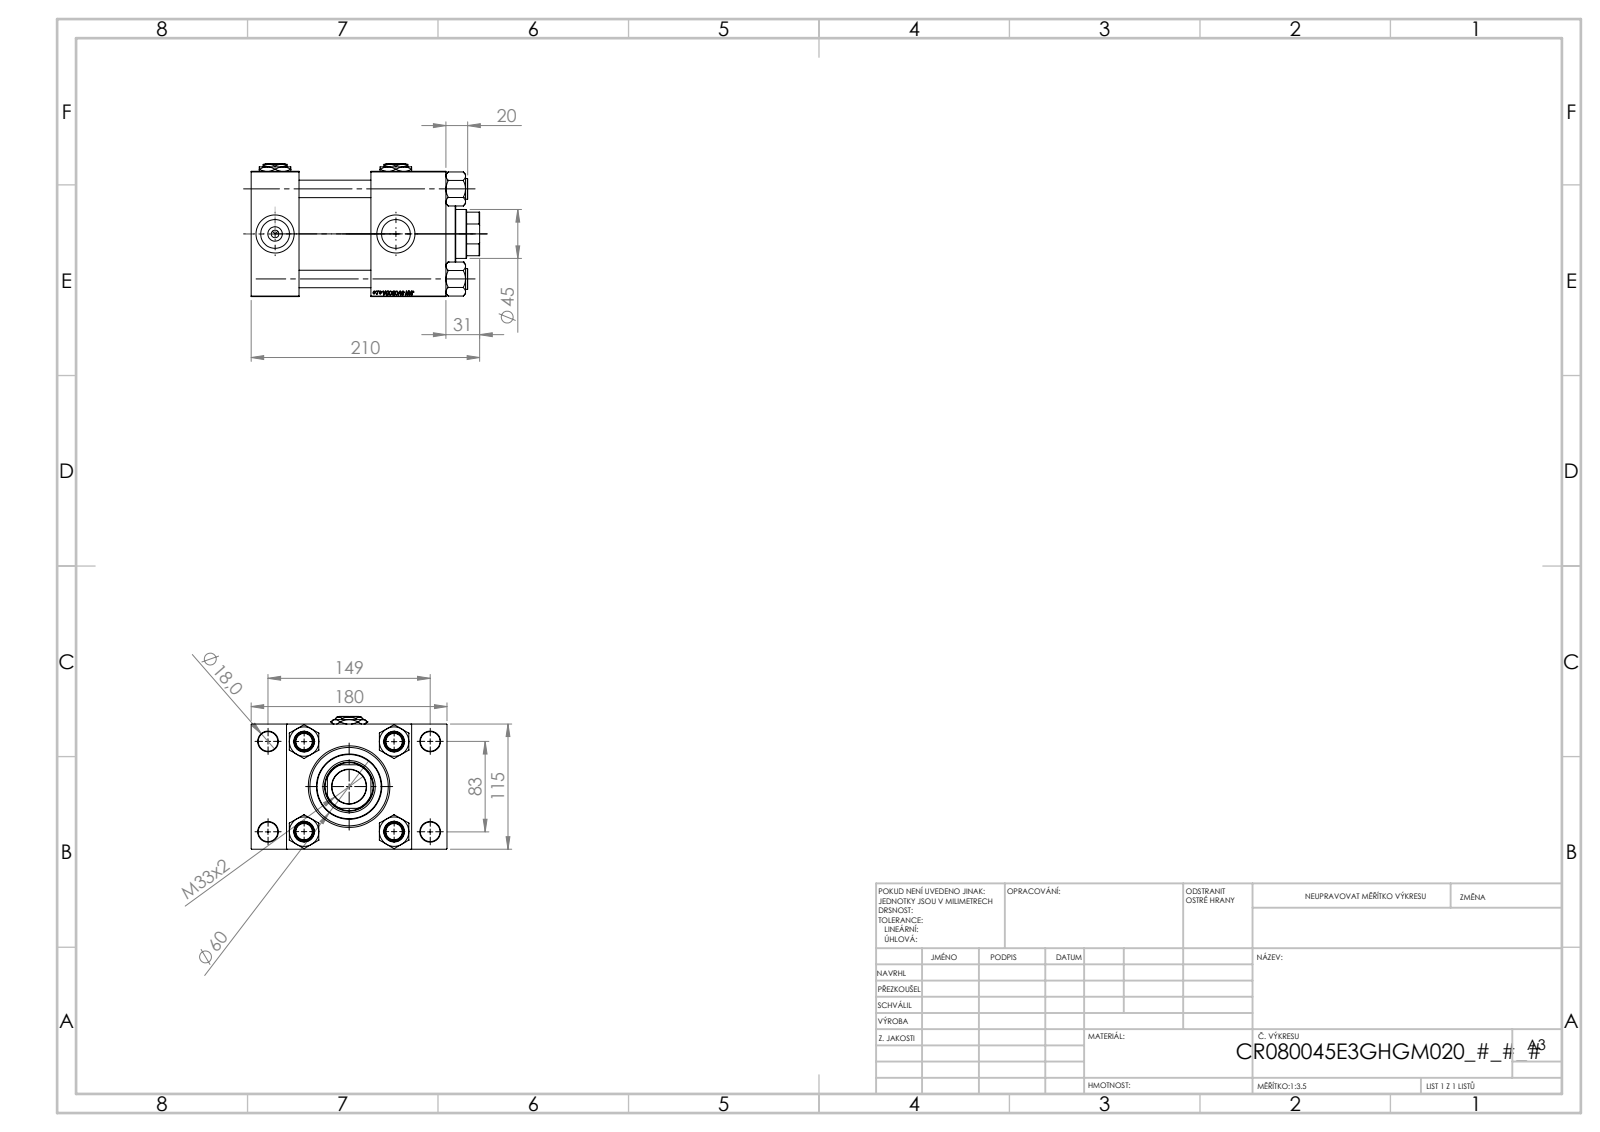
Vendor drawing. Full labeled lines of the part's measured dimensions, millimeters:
Part name (STEP PRODUCT): V215CR_VCP_E; V215CR_TYCINKA_E; Zatka_pro_OIL_PORT; NUT_M5_E (+2 more)
STEP written by: SolidWorks 2019 (CONFIG_CONTROL_DESIGN)
Units: millimetres
Bodies: 13 solids, 1290 faces (595 planar, 101 cylindrical, 594 other)
Overall size (bounding box): 210 × 180 × 122
Volume: 2 103 000 mm³ · Surface area: 322 824 mm²
Round holes (diameter × count): ⌀16 ×4, ⌀18 ×4, ⌀26.44 ×4, ⌀35 ×4, ⌀7 ×3, ⌀2.5 ×2, ⌀31.5 ×1, ⌀45 ×1, ⌀48 ×1, ⌀61 ×1, ⌀72 ×1, ⌀80 ×1
Round bosses / shafts (diameter × count): ⌀19 ×4, ⌀86 ×1, ⌀60 ×1
Partial cylindrical surfaces — rounded edges, fillets, slot ends (radius × count): R22 ×1
Main face-to-face distances: 115, 44, 179, 135, 32.5, 147.5, 110, 69, 66, 20
Hole centre spacings: 33.15, 41.96, 57.81, 58.48, 82.7, 85.28, 86.17, 89.24
